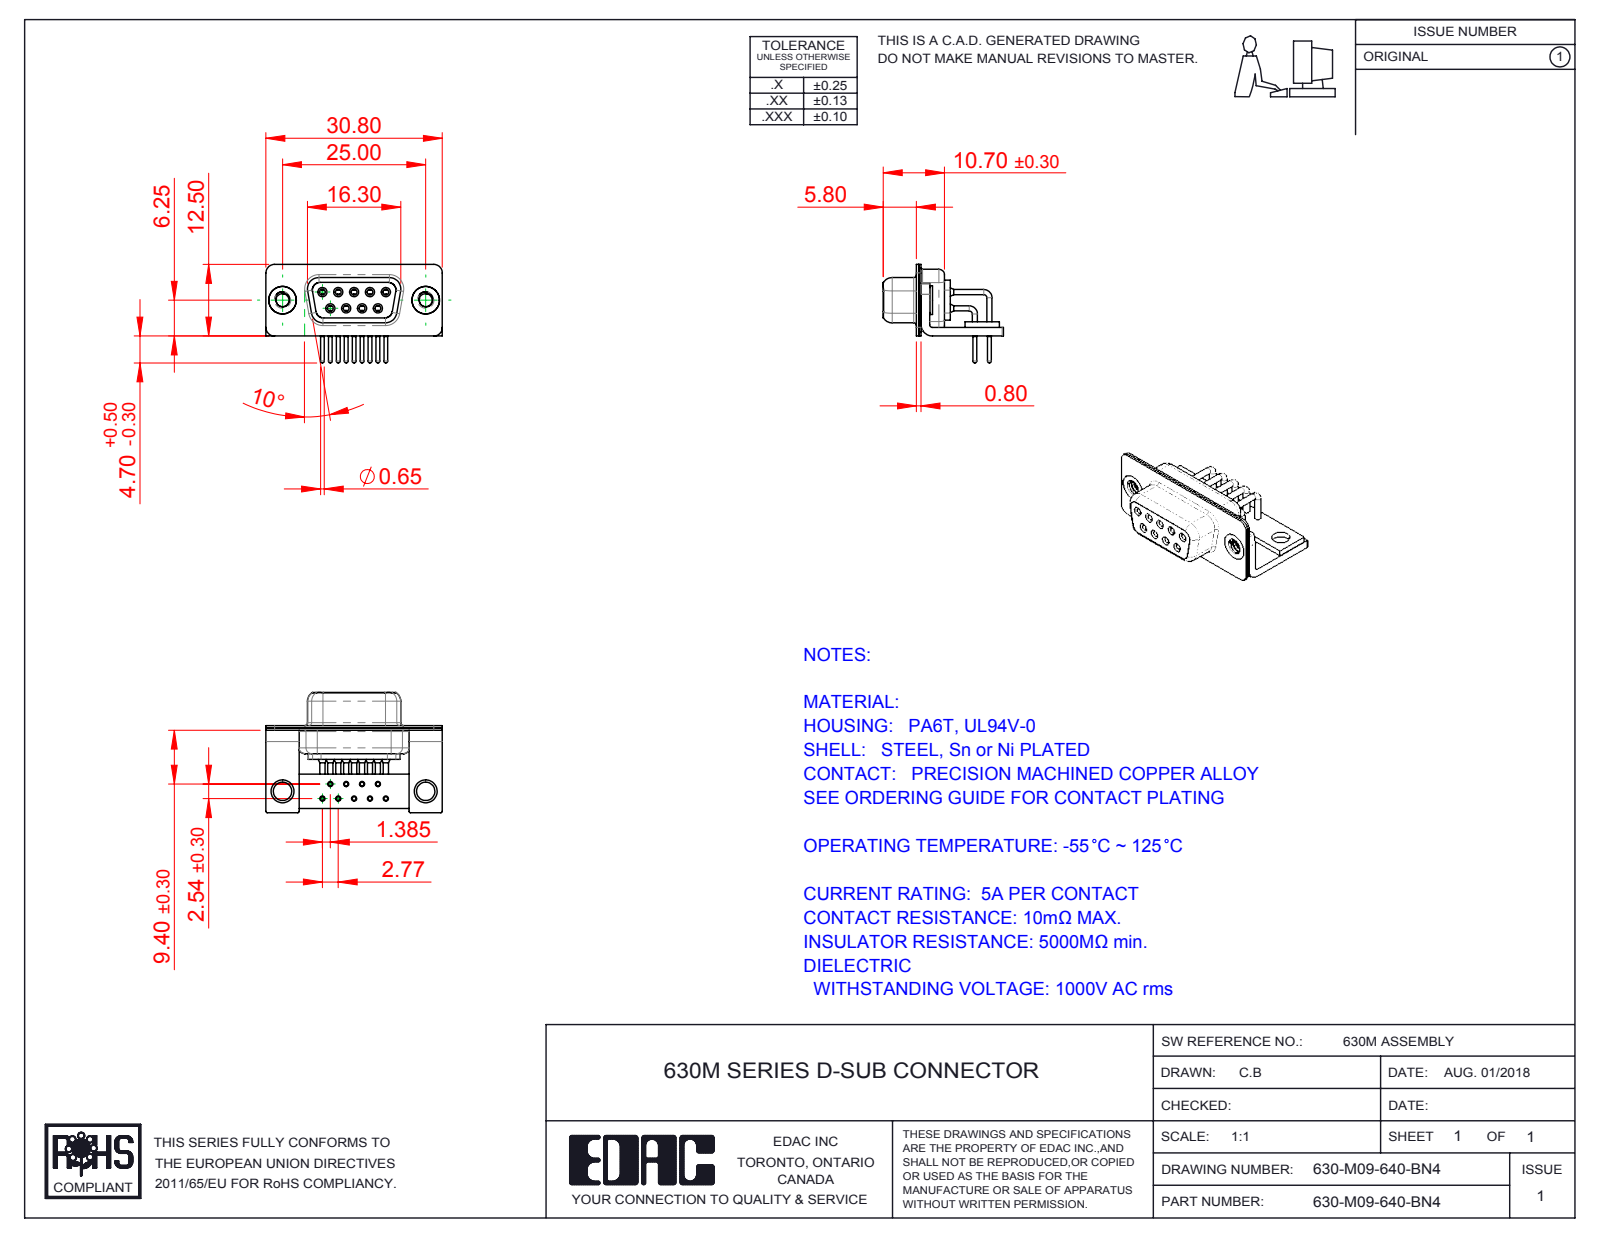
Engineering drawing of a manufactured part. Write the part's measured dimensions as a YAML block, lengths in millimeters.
part_name: "630M Housing_09 Contacts; 630M Shell Front_09 Contacts; 630M Contact Row 1; 630-M09-640-BN4 (+5 more)"
step_written_by: "SolidWorks 2016 (CONFIG_CONTROL_DESIGN)"
units: millimeters
bodies: {solids: 17, faces: 824, planar: 228, cylindrical: 384, other: 212}
overall_size: [30.8, 21, 17.2]
volume: 2191
surface_area: 5674
round_holes:
  - {diameter: 0.9, count: 9}
  - {diameter: 1, count: 9}
  - {diameter: 1.1, count: 9}
  - {diameter: 1.7, count: 9}
  - {diameter: 1.8, count: 9}
  - {diameter: 2, count: 9}
  - {diameter: 2.26, count: 2}
  - {diameter: 3.2, count: 2}
  - {diameter: 4, count: 2}
  - {diameter: 4.8, count: 2}
round_bosses_or_shafts:
  - {diameter: 1.6, count: 9}
  - {diameter: 1.5, count: 9}
  - {diameter: 0.9, count: 9}
  - {diameter: 0.65, count: 9}
  - {diameter: 5, count: 2}
  - {diameter: 4.9, count: 2}
partial_cylinders:
  - {radius: 0.25, count: 16}
  - {radius: 1.5, count: 16}
  - {radius: 2, count: 13}
  - {radius: 1.35, count: 8}
  - {radius: 1.6, count: 8}
  - {radius: 0.5, count: 5}
  - {radius: 0.6, count: 4}
  - {radius: 0.65, count: 4}
face_to_face_distances: [0.4, 0.8, 1.5, 2.3, 1.9, 1, 9.35, 1.45, 2.5, 8.95]
hole_center_spacings: [2.77, 5.54, 3.16, 4.87, 8.31, 2.89, 2.9, 5.03]
